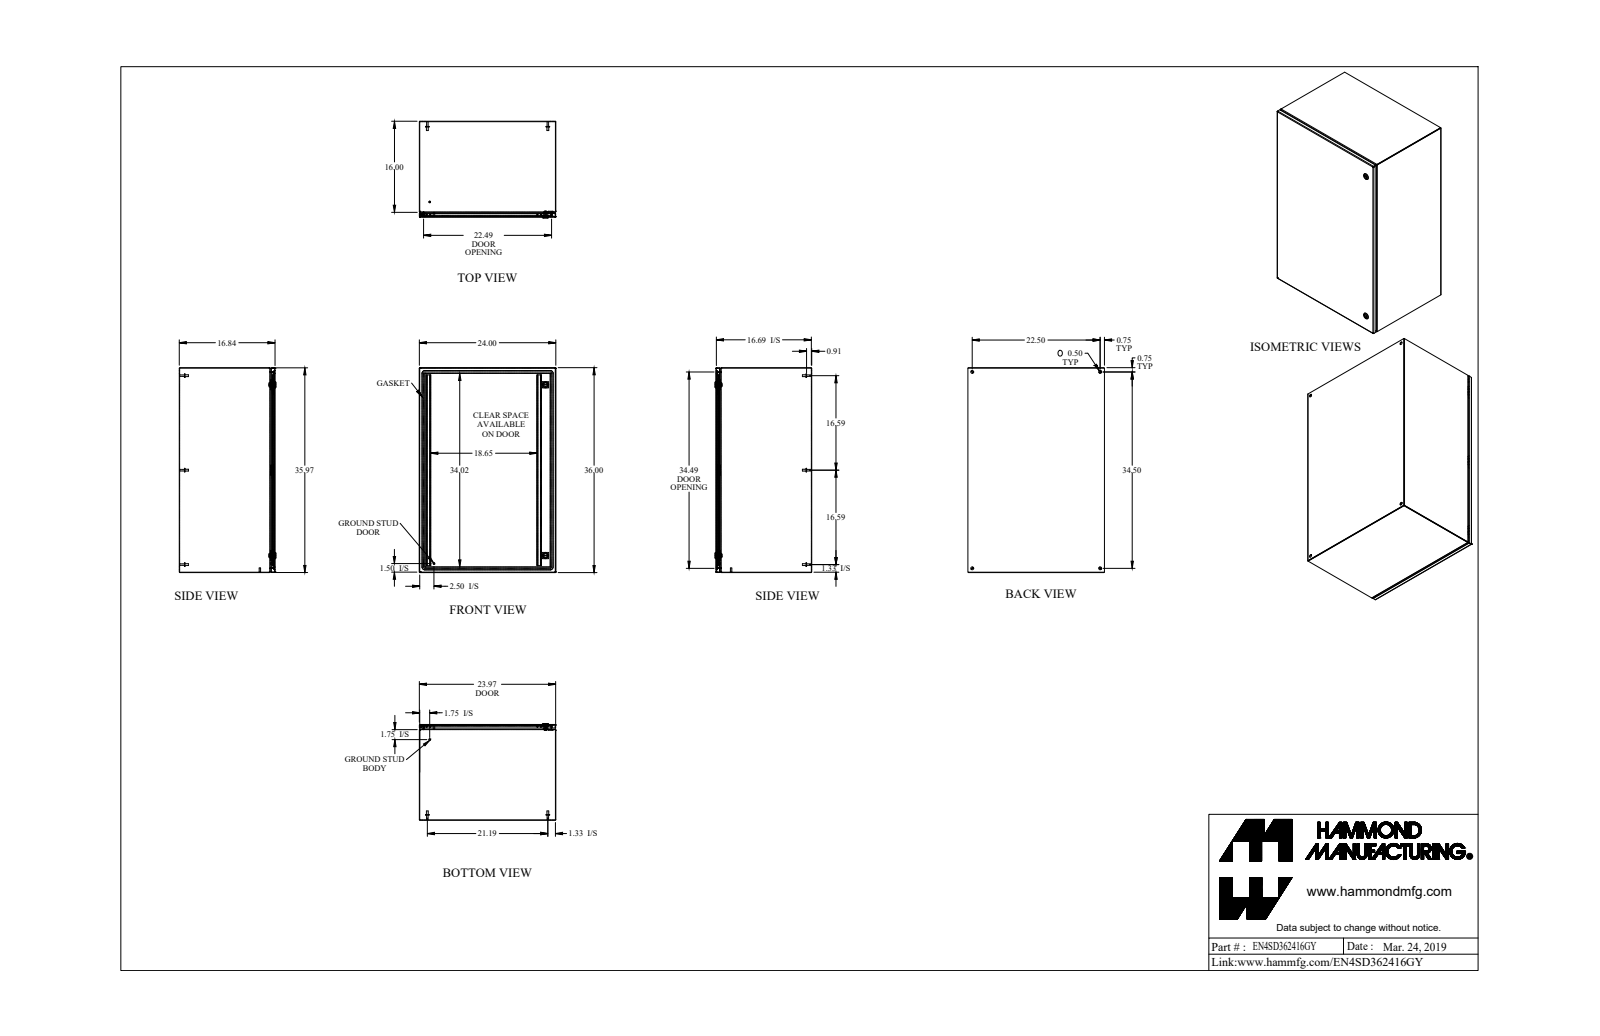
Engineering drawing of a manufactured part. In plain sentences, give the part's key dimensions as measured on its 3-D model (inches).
The part is named "EN4SD362416GY". Its 3-D file was written by "SolidWorks 2019 (AUTOMOTIVE_DESIGN)". It is 35 solids with 901 faces: 434 planar, 295 cylindrical and 172 other. Overall it measures 36 by 24 by 16.997 inches. Its volume is 295.5 cubic inches and its surface area 8 291 square inches. Round holes: 4 of diameter 0.5, 2 of diameter 0.232, 2 of diameter 0.625, 2 of diameter 0.785, 1 of diameter 0.172, 1 of diameter 0.24, 1 of diameter 0.242. Round bosses or shafts: 6 of diameter 0.625, 6 of diameter 0.313, 6 of diameter 0.27, 2 of diameter 1.1, 2 of diameter 0.525, 2 of diameter 0.281, 2 of diameter 0.25, 1 of diameter 0.455. Partial cylindrical surfaces (rounded edges, fillets, slot ends): 18 of radius 0.036, 18 of radius 0.108, 12 of radius 0.043, 12 of radius 0.081, 12 of radius 0.312, 6 of radius 0.006, 6 of radius 0.062, 4 of radius 0.125. The main face-to-face distances are 0.072, 16.765, 23.928, 16.693, 16.837, 35.928, 23.856, 24, 35.856, 36. The hole center spacings are 22.5, 34.5, 41.189, 2.493, 2.494, 21.544, 21.545, 29.999.
